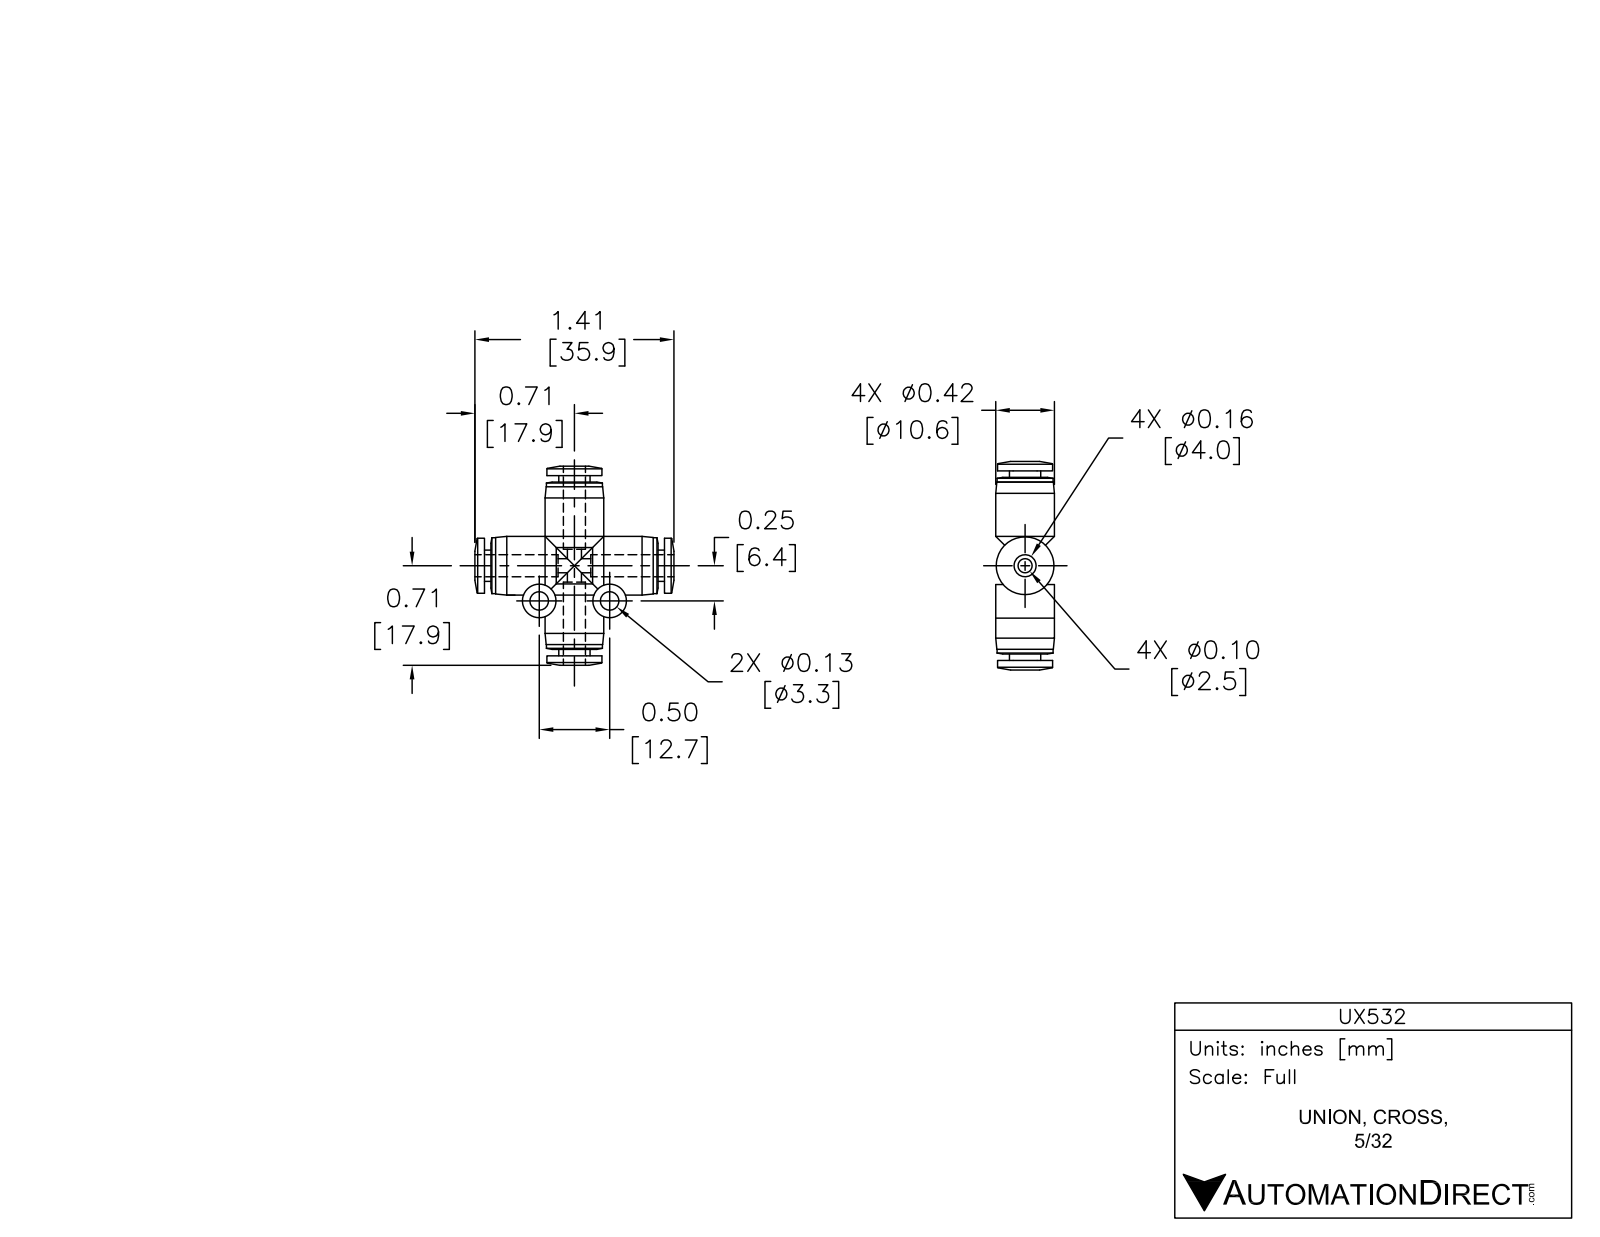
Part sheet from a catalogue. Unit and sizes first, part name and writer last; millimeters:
Units: millimetres
Overall size (bounding box): 37.3 × 35.6 × 10.5
Round holes (diameter × count): ⌀3 ×2, ⌀3.3 ×2, ⌀4.3 ×2
Round bosses / shafts (diameter × count): ⌀10.5 ×2, ⌀10 ×2, ⌀9.9 ×2, ⌀6.5 ×2, ⌀6 ×2, ⌀5.6 ×2
Main face-to-face distances: 1.1, 33.9, 32.7, 32.2, 31, 10.5, 13.1, 11.9, 20.8, 1.7
Hole centre spacings: 12.8
Volume: 4 080 mm³ · Surface area: 3 921 mm²
Bodies: 1 solid, 124 faces (26 planar, 66 cylindrical, 32 other)
Part name (STEP PRODUCT): UX532
STEP written by: SolidWorks 2018 (AUTOMOTIVE_DESIGN)
